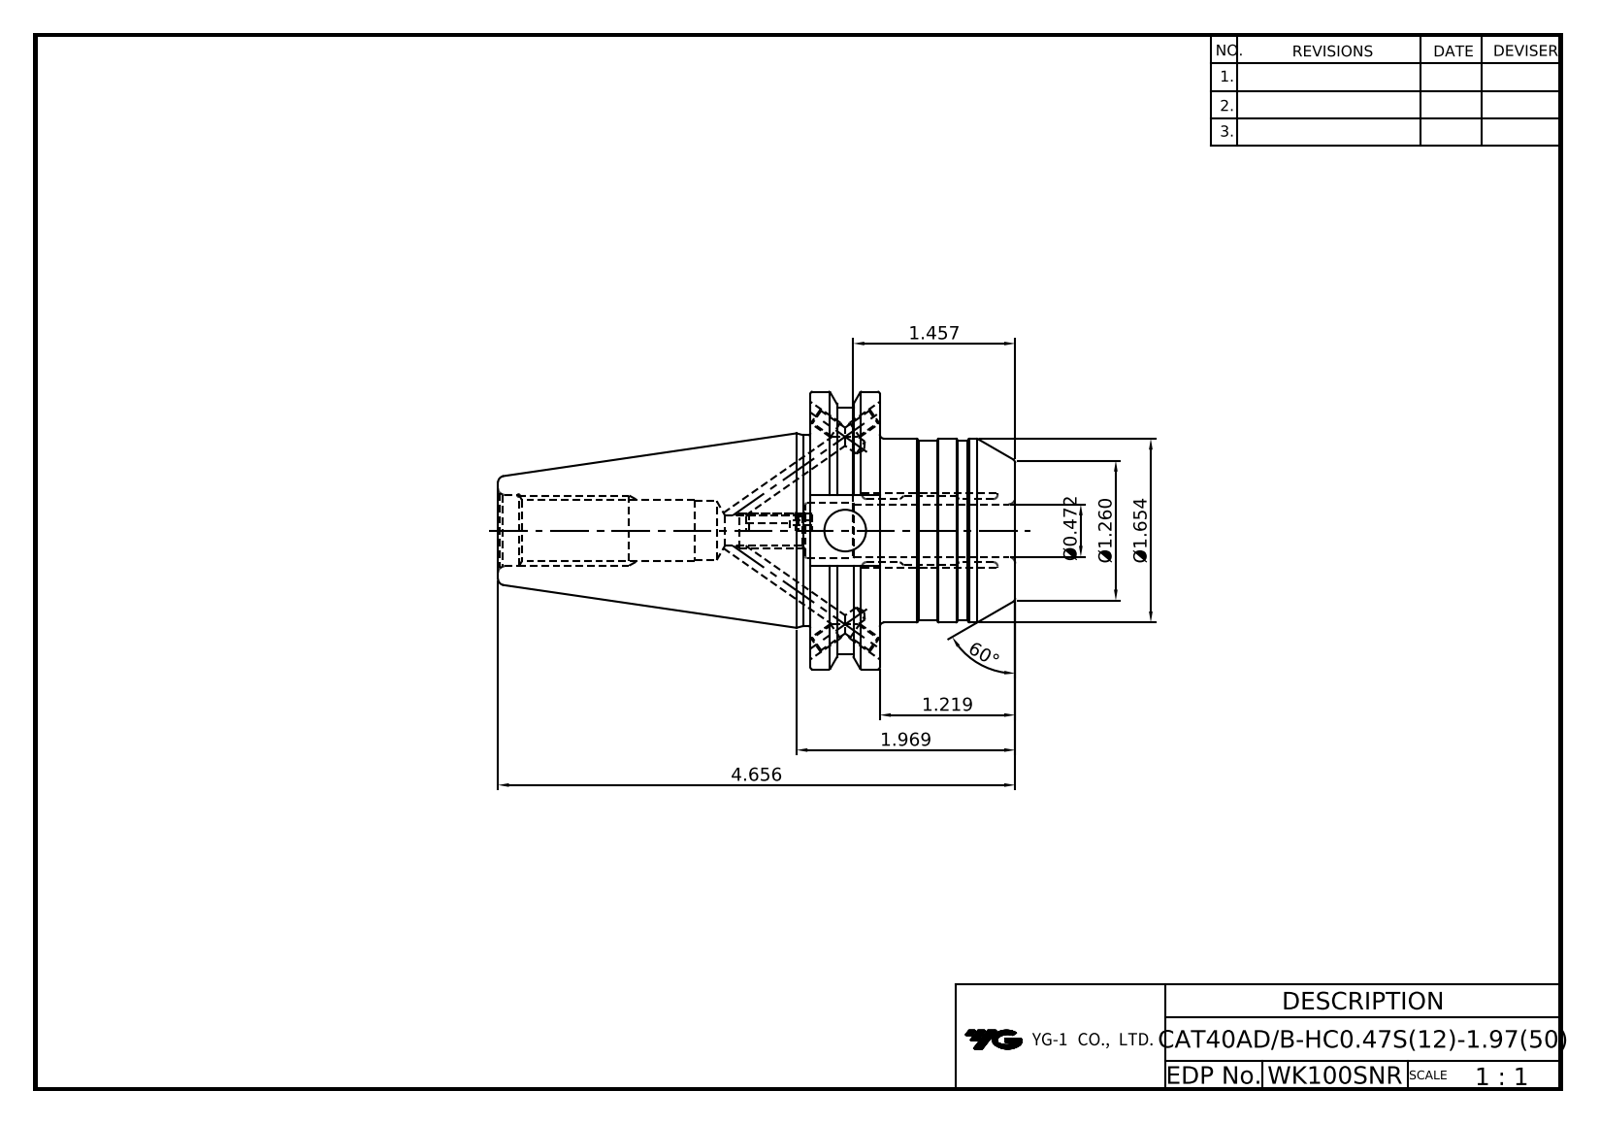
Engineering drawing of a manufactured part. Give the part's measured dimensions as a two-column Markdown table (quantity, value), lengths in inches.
| quantity | value |
| --- | --- |
| part name | LO-CAT40ADB-HC12S-50 |
| STEP written by | Autodesk Inventor 2025 (AUTOMOTIVE_DESIGN) |
| units | inches |
| bodies | 1 solid, 96 faces (33 planar, 30 cylindrical, 33 other) |
| overall size | 4.656 × 2.5 × 2.405 |
| volume | 8.474 in³ |
| surface area | 39.53 in² |
| round holes (diameter × count) | 0.128 × 4, 0.157 × 4, 0.272 × 1, 0.375 × 1, 0.472 × 1, 0.496 × 1, 0.527 × 1, 0.642 × 1 |
| round bosses / shafts (diameter × count) | 2.5 × 1, 2.217 × 1, 1.717 × 1, 1.654 × 1, 1.614 × 1 |
| main face-to-face distances | 0.625, 1.844, 1.219, 1.874, 0.645, 2.812, 3.437, 4.656, 3.05, 3.201 |
| hole center spacings | 1.383 |
